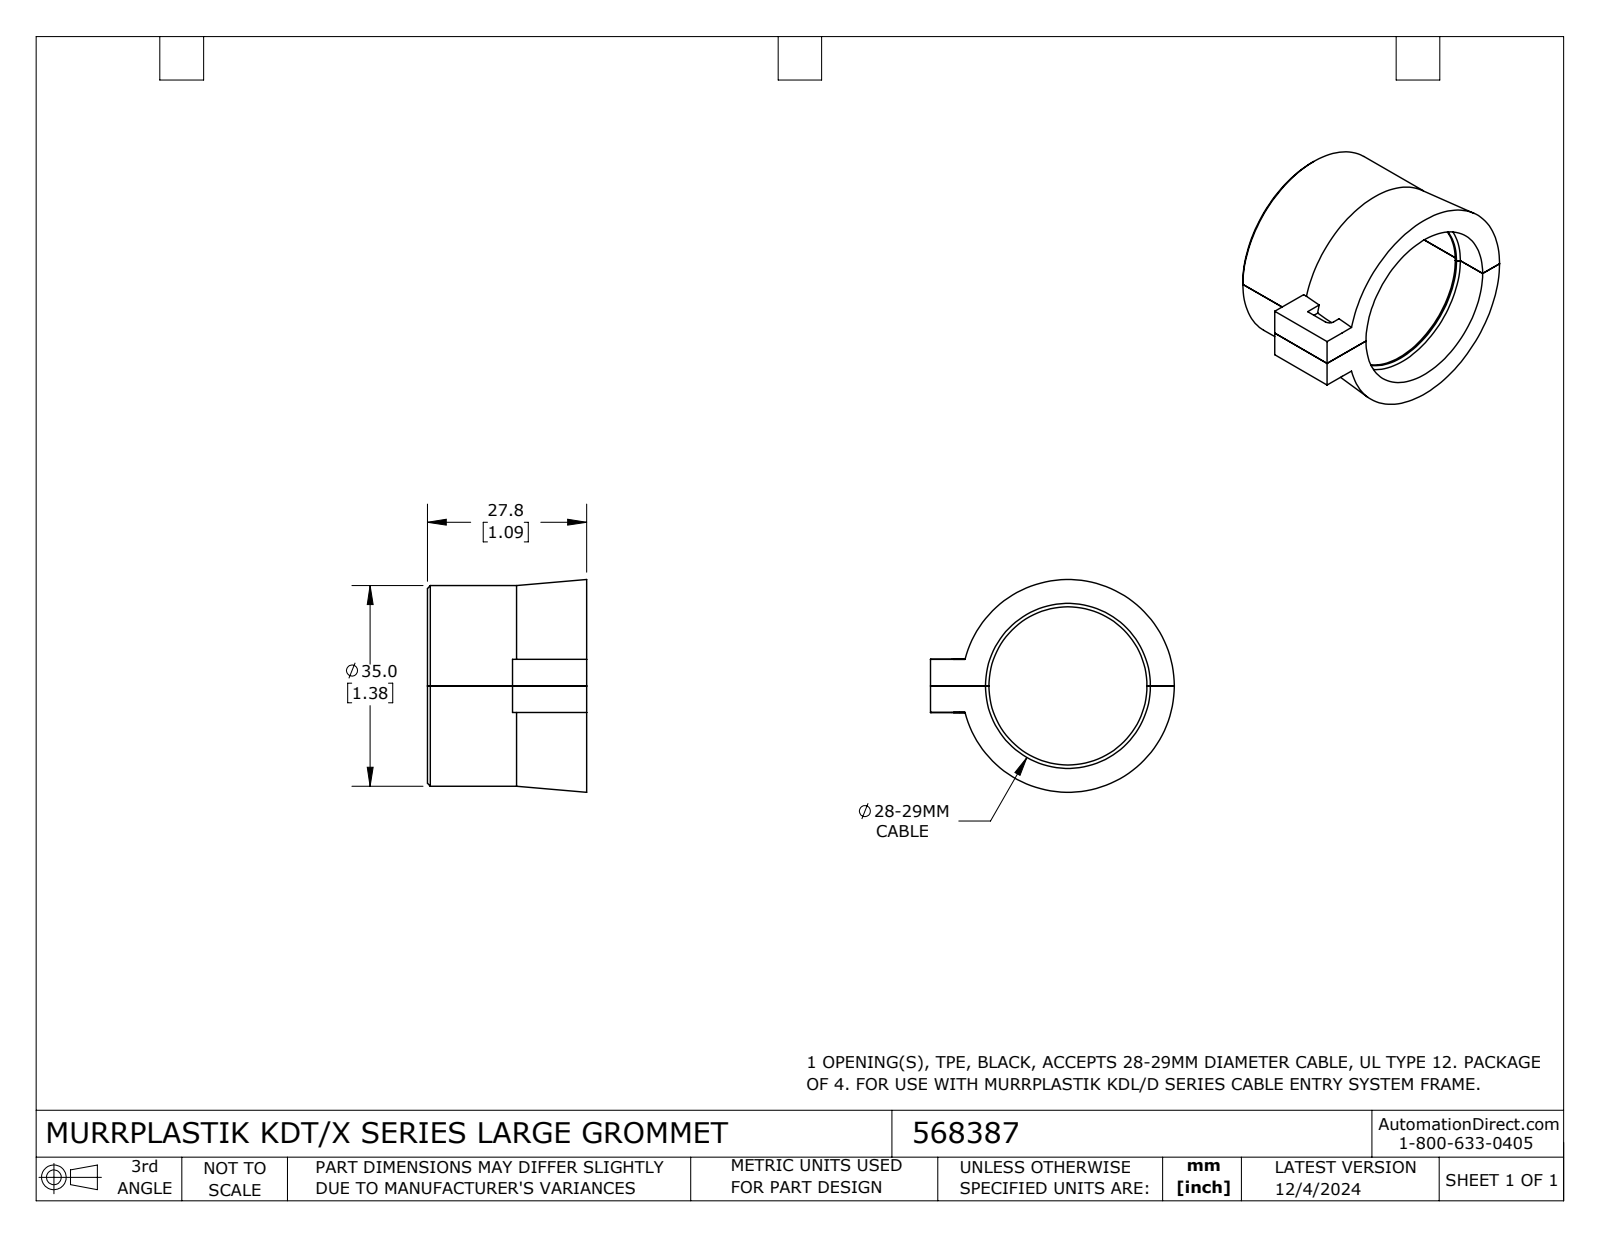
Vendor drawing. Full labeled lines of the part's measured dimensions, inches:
Part name (STEP PRODUCT): 568387
STEP written by: SolidWorks 2024 (AUTOMOTIVE_DESIGN)
Units: inches
Bodies: 2 solids, 46 faces (22 planar, 14 cylindrical, 10 other)
Overall size (bounding box): 1.676 × 1.462 × 1.094
Volume: 0.616 in³ · Surface area: 11.22 in²
Round holes (diameter × count): ⌀1.087 ×1, ⌀1.134 ×1
Round bosses / shafts (diameter × count): ⌀1.378 ×1
Partial cylindrical surfaces — rounded edges, fillets, slot ends (radius × count): R0.02 ×4, R0.039 ×1
Main face-to-face distances: 1.094, 0.183, 0.366, 0.51, 0.585, 0.061, 0.305, 0.122, 0.157, 0.243
